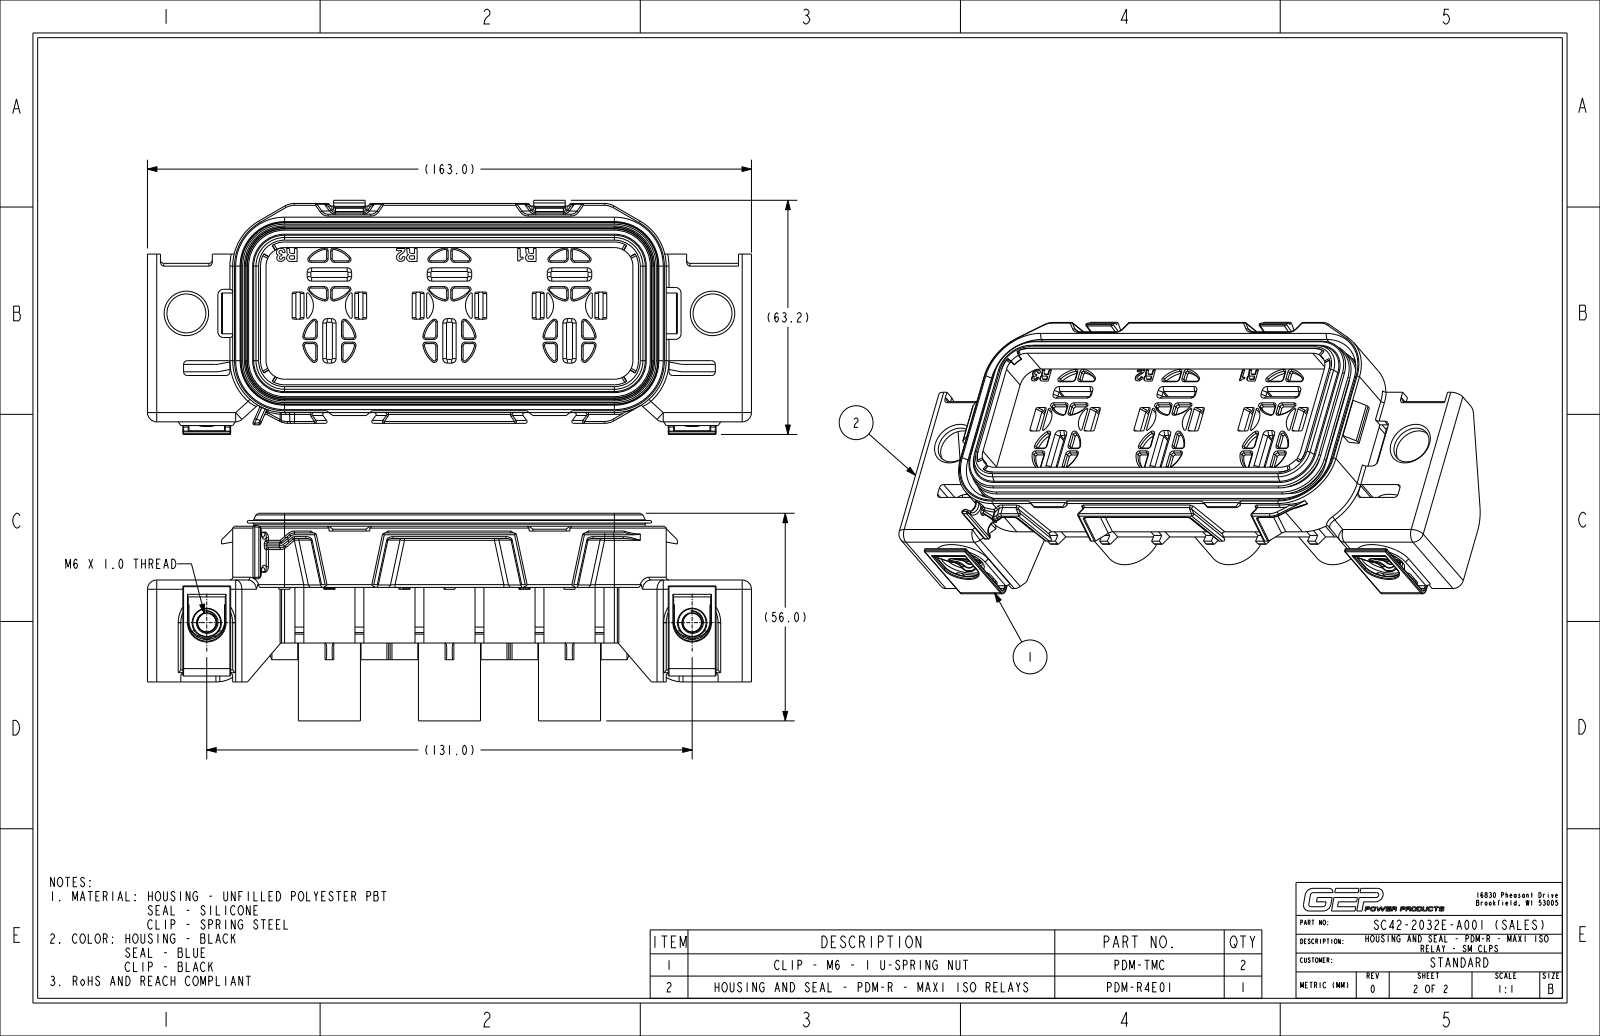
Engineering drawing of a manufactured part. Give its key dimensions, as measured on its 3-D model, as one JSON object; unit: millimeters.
{"part_name": "C26-1012-2E_SALES_NCF; C14-1013_INSTALLED_NCF; PDM-RS_INSTALLED_NCF_ASM; PDM-R4E01_NCF_ASM (+3 more)", "step_written_by": "CREO PARAMETRIC BY PTC INC, 2024014 (CONFIG_CONTROL_DESIGN)", "units": "millimeters", "bodies": {"solids": 4, "faces": 3291, "planar": 1448, "cylindrical": 958, "other": 885}, "overall_size": [163, 63.16, 56], "volume_mm3": 120492, "surface_area_mm2": 108156, "round_holes": [[9.8, 6], [13.75, 6], [10.5, 4], [5, 2], [7.5, 2], [12.5, 2]], "round_bosses_or_shafts": [[16.75, 3], [7, 2], [5, 1], [2.5, 1]], "partial_cylinders_radius": [[0.5, 237], [0.2, 92], [0.3, 82], [0.4, 76], [0.9, 39], [1, 26], [0.6, 24], [0.35, 16]], "face_to_face_distances": [1.5, 2, 38.5, 9.5, 37, 1.8, 11.5, 5.5, 9, 7], "hole_center_spacings": [32.4, 12.47, 13.24, 24.66, 25.05, 37.02, 42.46, 42.69]}
